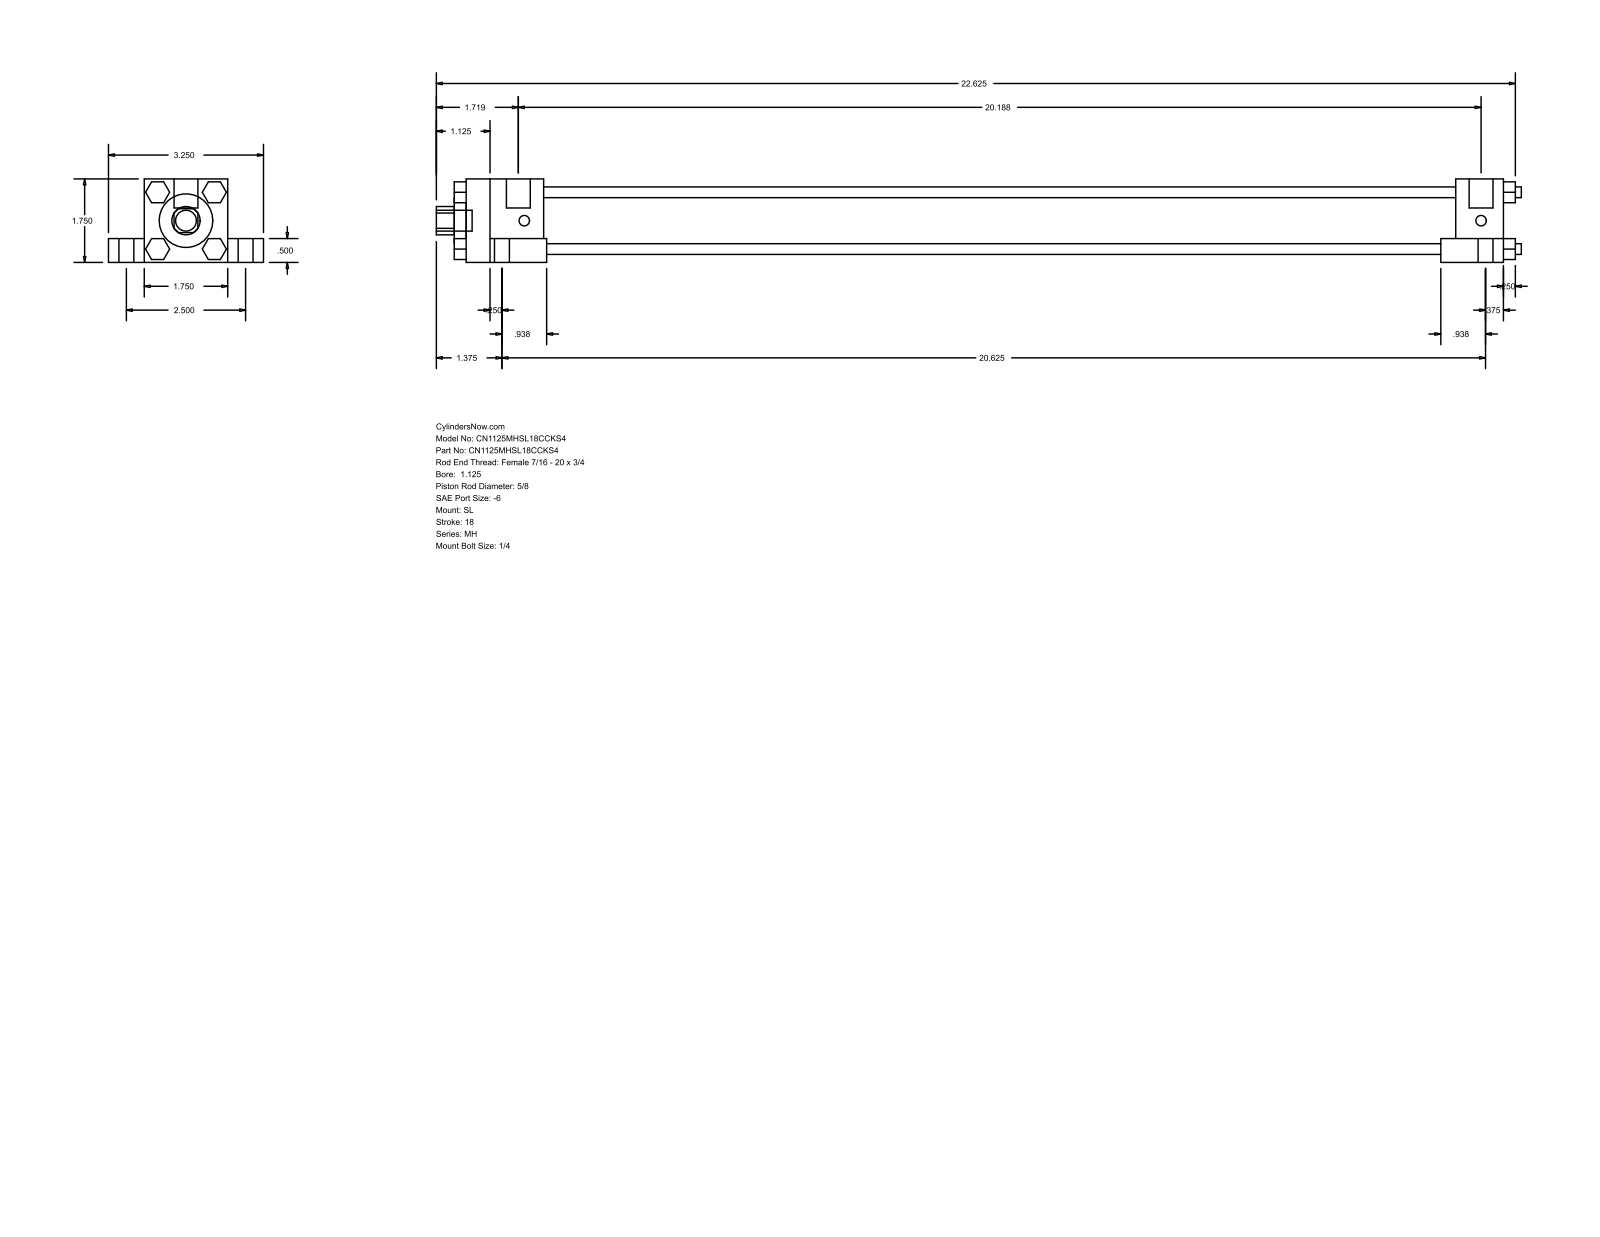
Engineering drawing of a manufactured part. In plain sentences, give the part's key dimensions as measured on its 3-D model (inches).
The part is named "MH_SL__0112_0.625". Its 3-D file was written by "GSSL Pune (CONFIG_CONTROL_DESIGN)". It is 0 solids with 150 faces: 114 planar, 36 cylindrical and 0 other. Overall it measures 22.75 by 3.25 by 1.75 inches. Round holes: 1 of diameter 0.625, 1 of diameter 1.125, 1 of diameter 1.375. Round bosses or shafts: 4 of diameter 0.563, 4 of diameter 0.313, 4 of diameter 0.225, 4 of diameter 0.219, 2 of diameter 0.5, 1 of diameter 0.437. Partial cylindrical surfaces (rounded edges, fillets, slot ends): 1 of radius 0.297. The main face-to-face distances are 1.75, 0.75, 0.5, 1.25, 2.5, 0.437, 1.313, 19.938, 19.125, 20.125.
